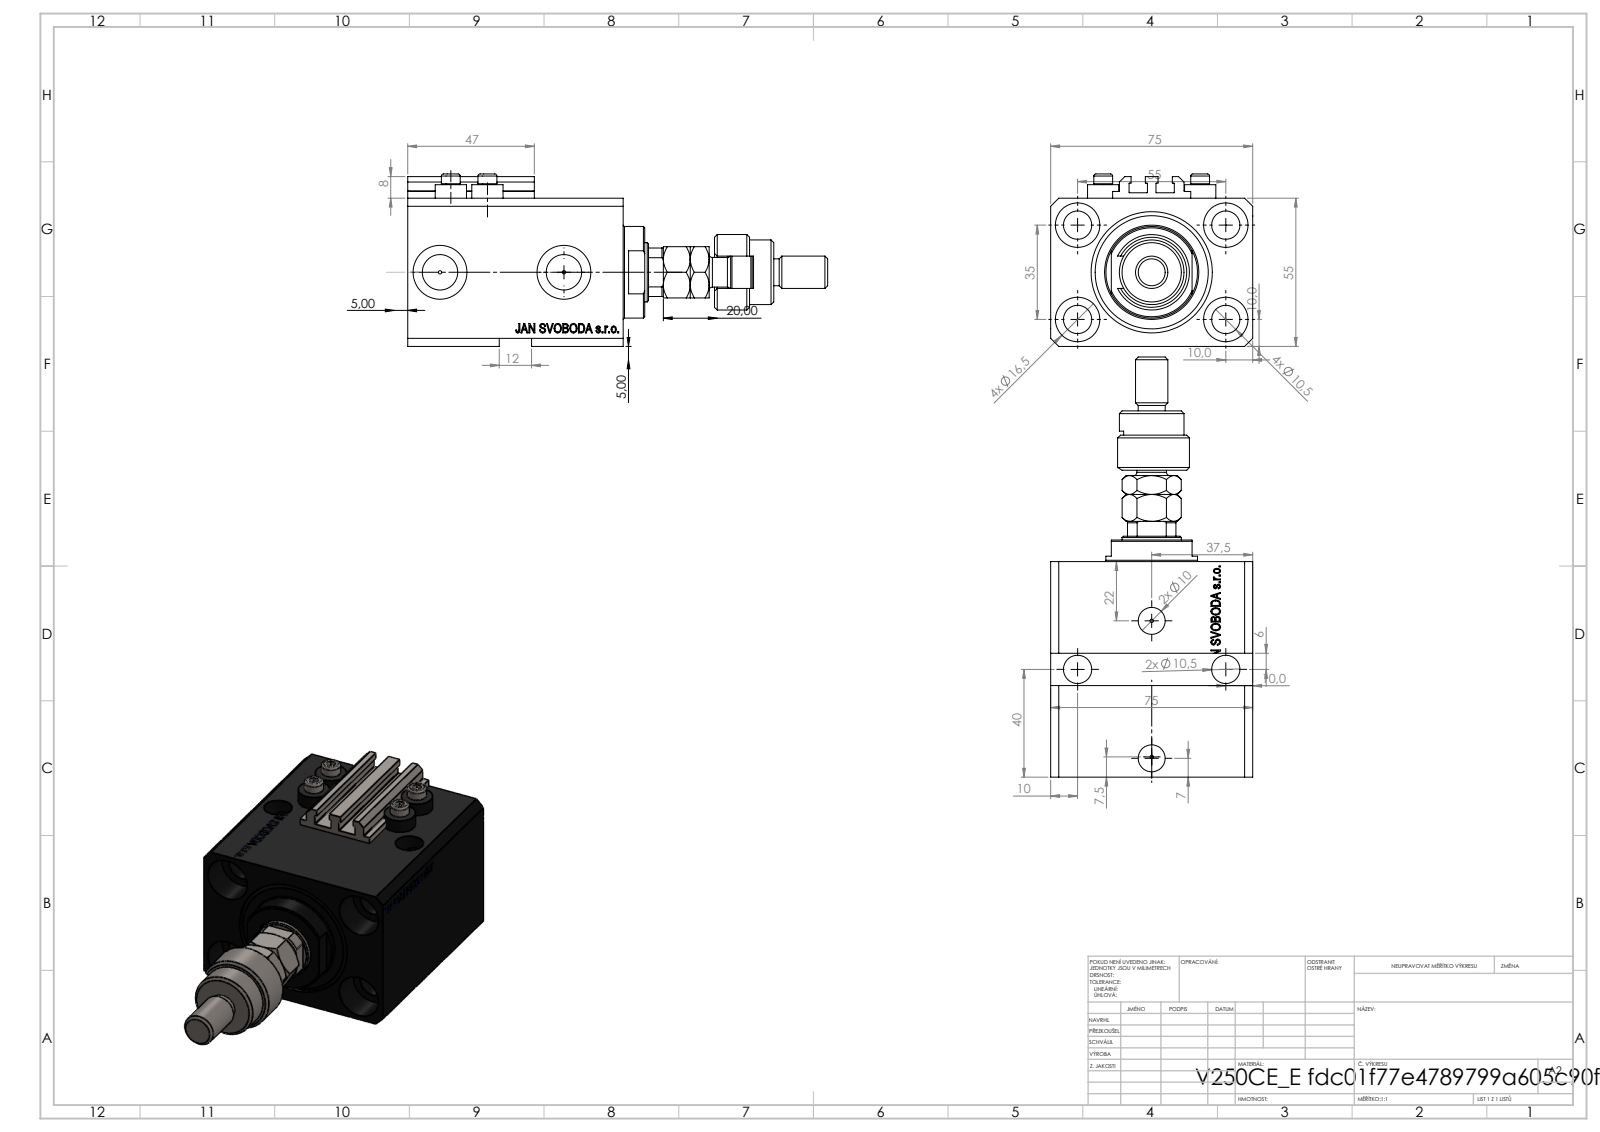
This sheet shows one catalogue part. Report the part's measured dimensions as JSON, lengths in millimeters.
{"part_name": "V250CE_C_VCP; FEMALE_PART_FOR_DFA; V250CE_VC_E; ALLEN BOLT V250CE (+2 more)", "step_written_by": "SolidWorks 2019 (CONFIG_CONTROL_DESIGN)", "units": "millimeters", "bodies": {"solids": 10, "faces": 1149, "planar": 542, "cylindrical": 139, "other": 468}, "overall_size": [156, 75, 64], "volume_mm3": 301774, "surface_area_mm2": 81585, "round_holes": [[10.5, 7], [1.25, 4], [4, 4], [16.5, 4], [10, 2], [13.16, 2], [20, 2], [22, 1], [32, 1], [45, 1]], "round_bosses_or_shafts": [[11.6, 4], [7, 4], [34, 1], [28, 1], [24, 1], [18, 1], [12, 1], [11, 1]], "partial_cylinders_radius": [[0.2, 10], [9.75, 1], [10.5, 1]], "face_to_face_distances": [55, 75, 15, 80, 65, 3, 55.1, 9.9, 70.1, 8], "hole_center_spacings": [32.6, 55, 13.6, 14.09, 19.89, 20.12, 25.81, 28.48]}
